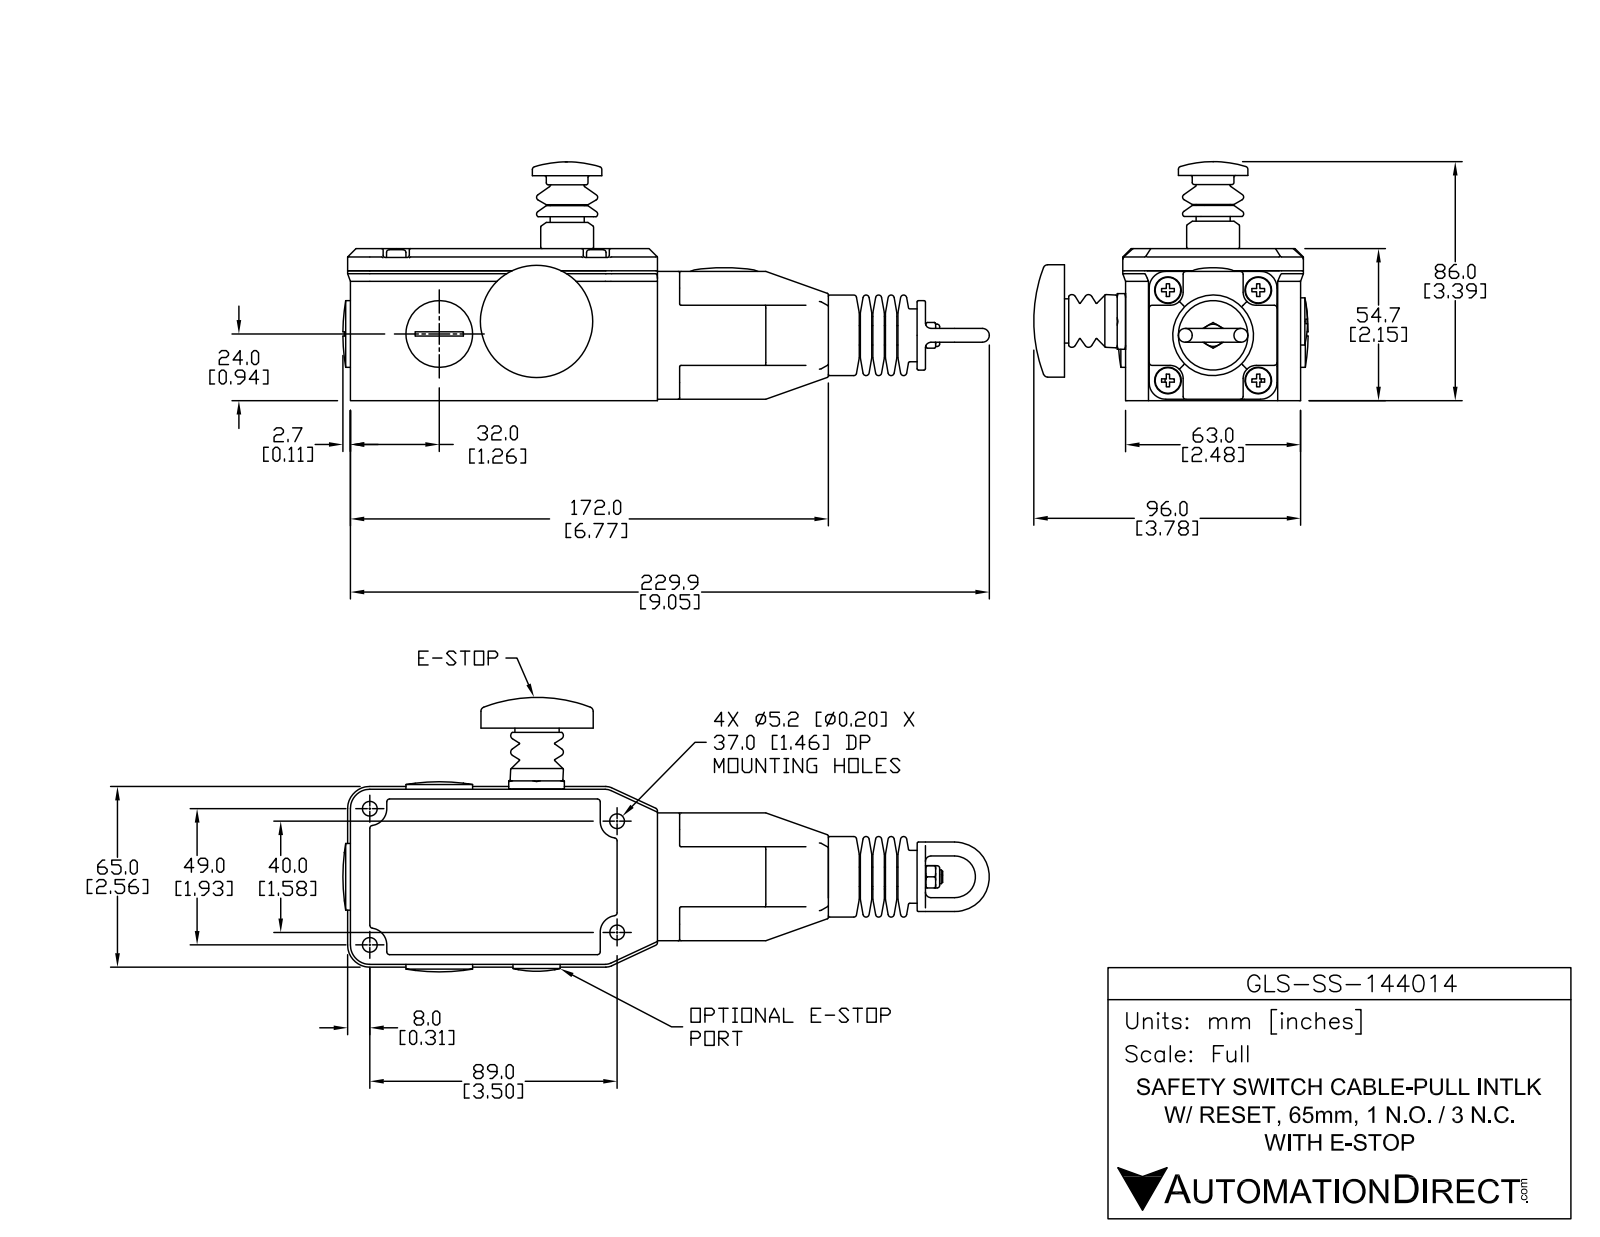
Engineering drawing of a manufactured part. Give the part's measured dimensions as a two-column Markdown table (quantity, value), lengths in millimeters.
| quantity | value |
| --- | --- |
| part name | GLS-SS-144014 |
| STEP written by | SolidWorks 2013 (AUTOMOTIVE_DESIGN) |
| units | millimeters |
| bodies | 2 solids, 664 faces (201 planar, 230 cylindrical, 233 other) |
| overall size | 233.8 × 104.37 × 86 |
| volume | 510 903 mm³ |
| surface area | 62 560 mm² |
| round holes (diameter × count) | 5.2 × 4, 9.5 × 4 |
| round bosses / shafts (diameter × count) | 9.2 × 4, 6 × 4, 26.8 × 2, 25 × 2, 19 × 2, 5 × 2, 40 × 1, 29 × 1 |
| partial cylindrical surfaces (radius × count) | 0.5 × 74, 0.75 × 20, 1 × 8, 3 × 4, 4.5 × 4, 4.8 × 4, 5 × 4, 16 × 4 |
| main face-to-face distances | 54.4, 65, 54.7, 11.7, 33.3, 45, 90.65, 25.65, 4.5, 50.2 |
| hole center spacings | 32.5, 32.6, 46.03, 89.11, 99.51, 40, 49 |
